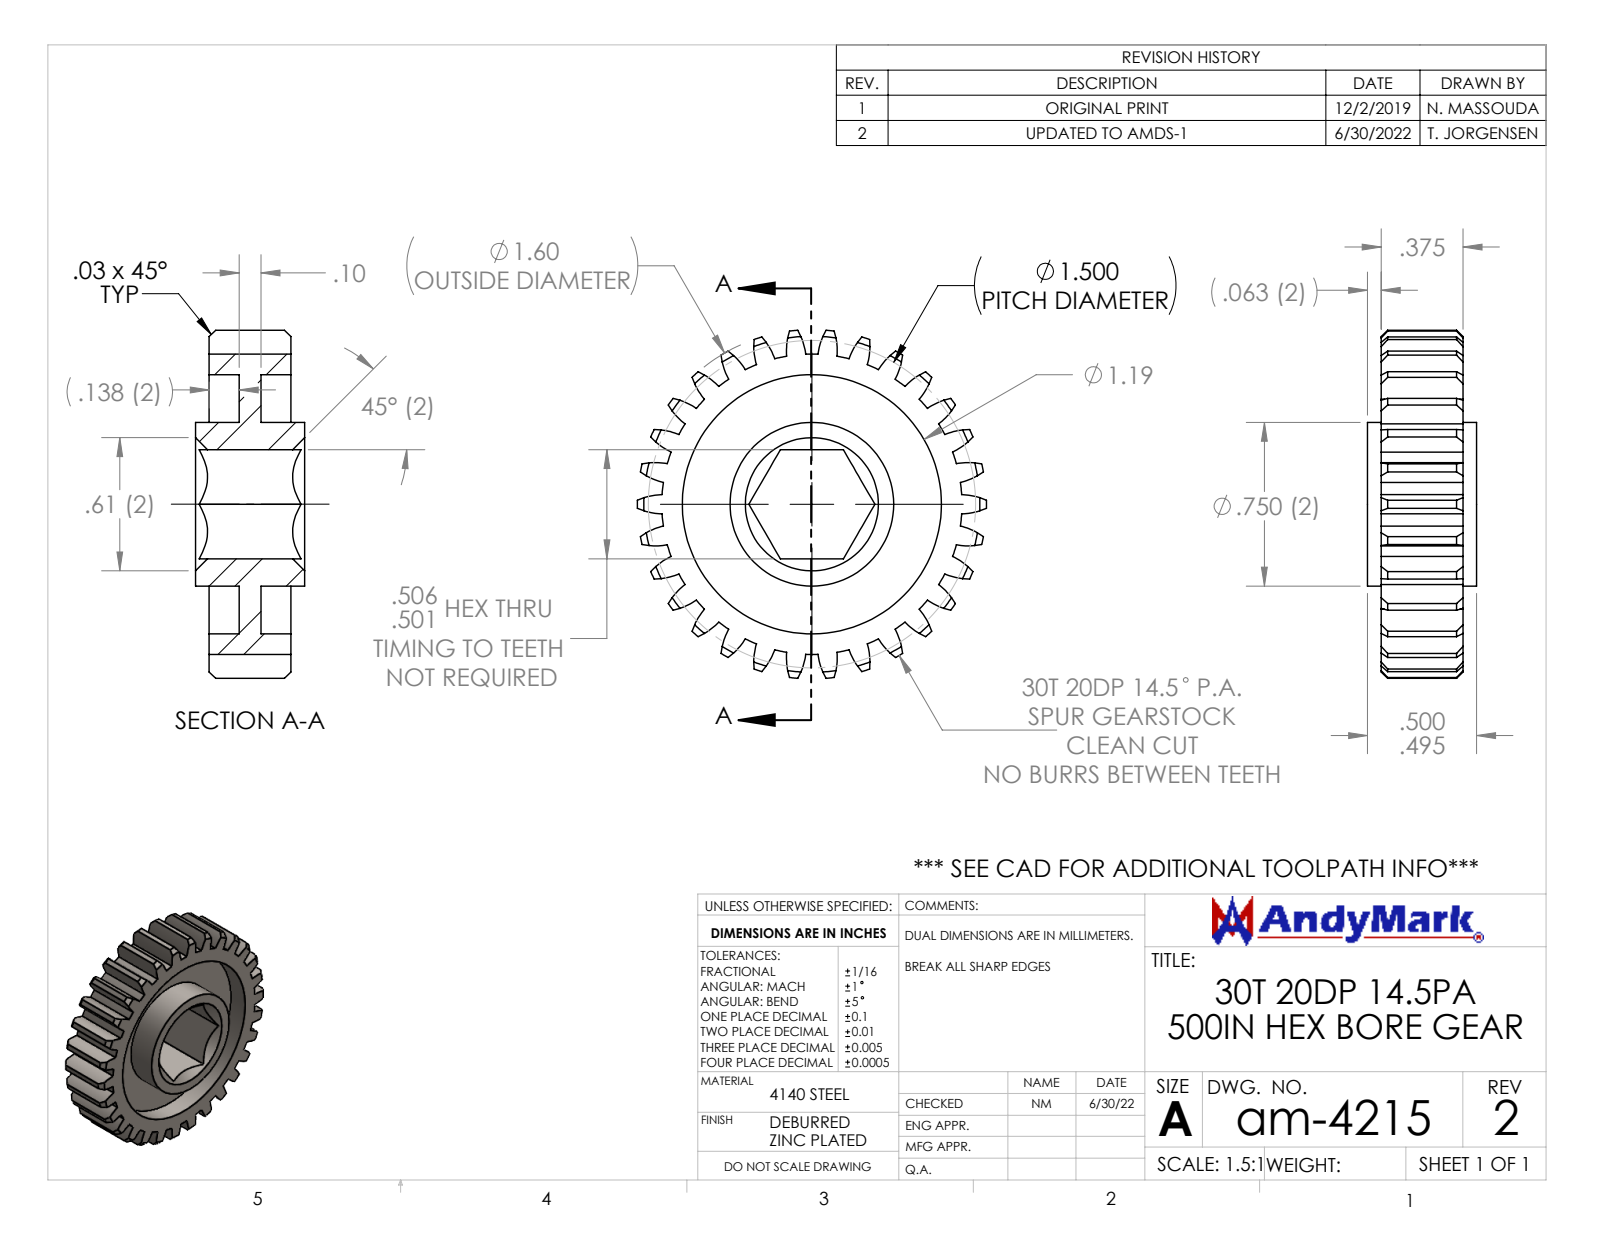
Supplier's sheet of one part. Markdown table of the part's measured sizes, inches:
| quantity | value |
| --- | --- |
| part name | am-4215 30T 20DP 500hex 375 FW |
| STEP written by | SolidWorks 2022 (CONFIG_CONTROL_DESIGN) |
| units | inches |
| bodies | 1 solid, 209 faces (12 planar, 133 cylindrical, 64 other) |
| overall size | 1.6 × 1.595 × 0.5 |
| volume | 0.406 in³ |
| surface area | 9.358 in² |
| round holes (diameter × count) | 1.187 × 1 |
| round bosses / shafts (diameter × count) | 0.75 × 1 |
| partial cylindrical surfaces (radius × count) | 0.3 × 60, 0.688 × 1, 0.8 × 1 |
| main face-to-face distances | 0.1, 0.137, 0.237, 0.375, 0.238, 0.138, 0.5, 0.2, 0.3, 0.063 |
